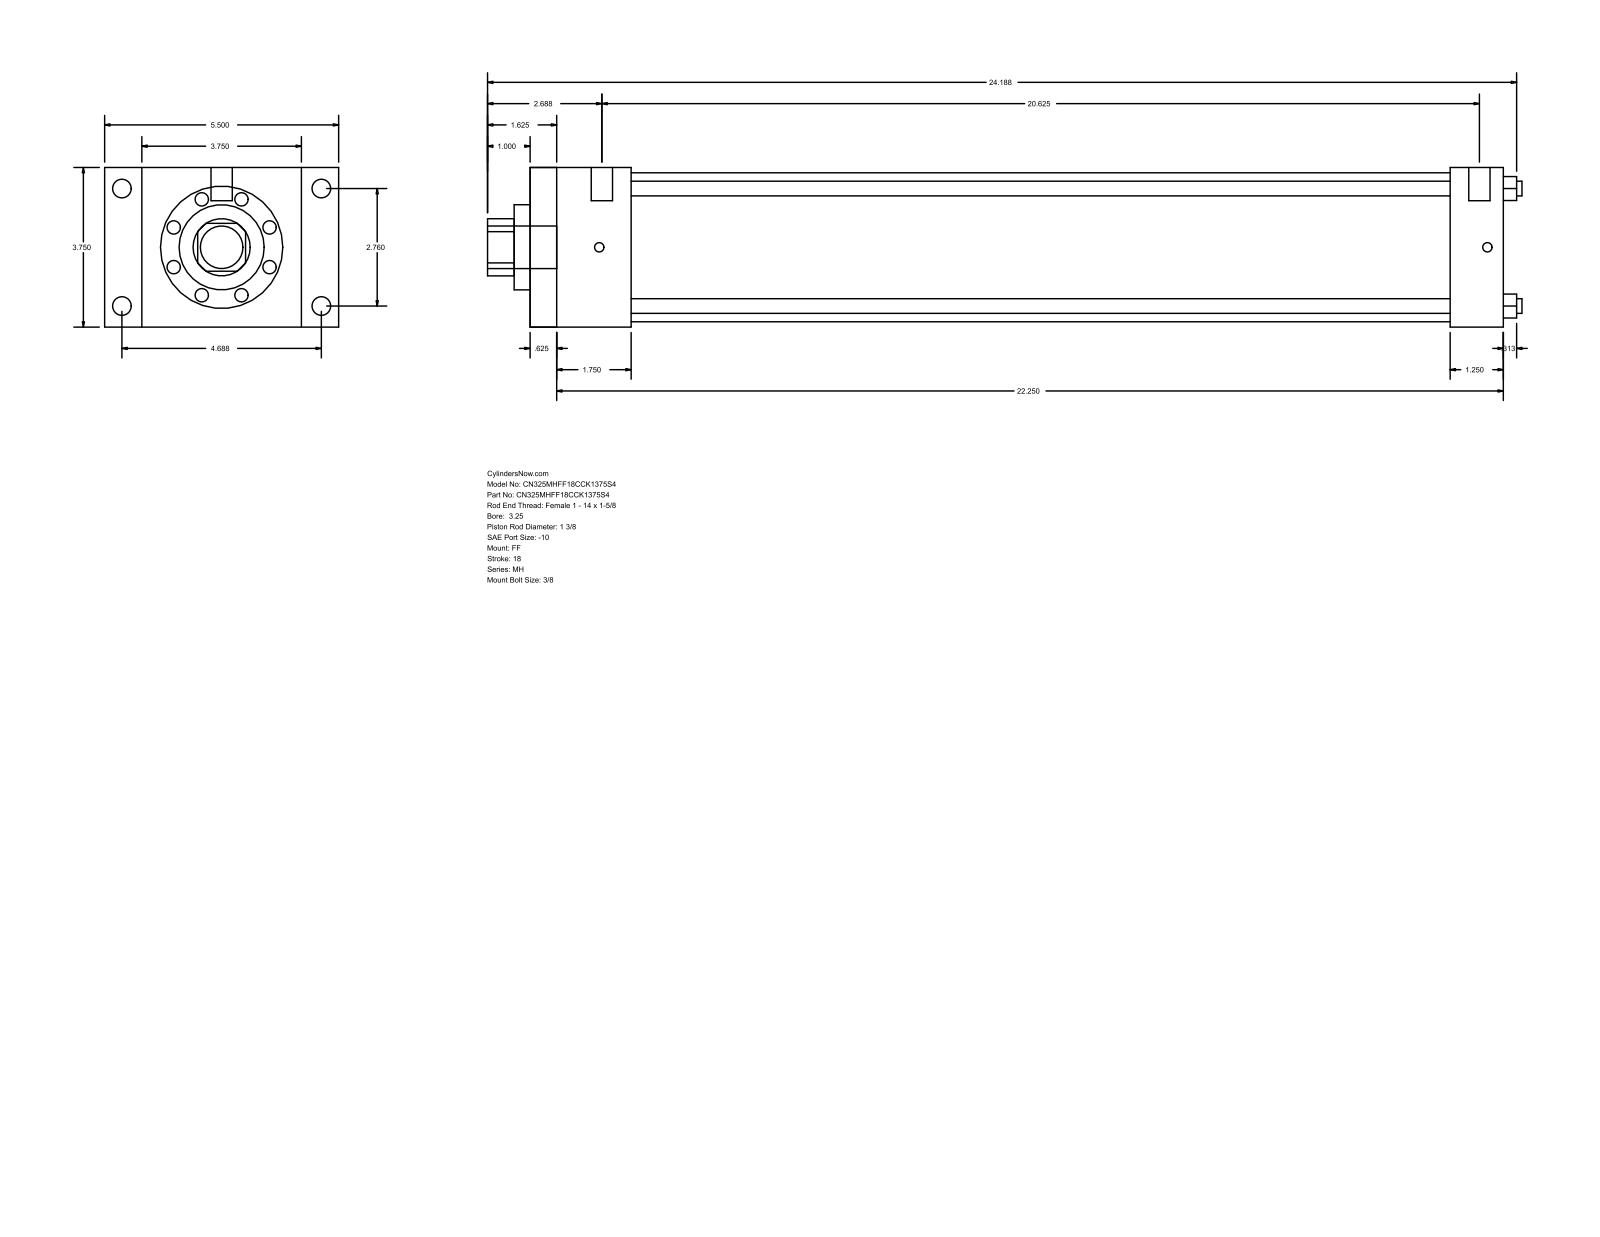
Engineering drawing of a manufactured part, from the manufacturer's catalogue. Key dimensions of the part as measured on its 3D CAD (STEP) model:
Part name (STEP PRODUCT): MH_FF__0325_1.375
STEP written by: GSSL Pune (CONFIG_CONTROL_DESIGN)
Units: millimetres
Bodies: 0 solids, 92 faces (64 planar, 28 cylindrical, 0 other)
Overall size (bounding box): 617.54 × 139.7 × 95.25
Round holes (diameter × count): ⌀8.76 ×4, ⌀34.92 ×1, ⌀50.8 ×1, ⌀88.9 ×1
Round bosses / shafts (diameter × count): ⌀11.13 ×4, ⌀5.56 ×4, ⌀12.7 ×2, ⌀25.4 ×1
Partial cylindrical surfaces — rounded edges, fillets, slot ends (radius × count): R17.06 ×1
Main face-to-face distances: 95.24, 581.02, 15.87, 565.15, 22.23, 117.47, 549.27, 533.4, 31.75, 60.32
Hole centre spacings: 49.57, 70.1, 99.14
